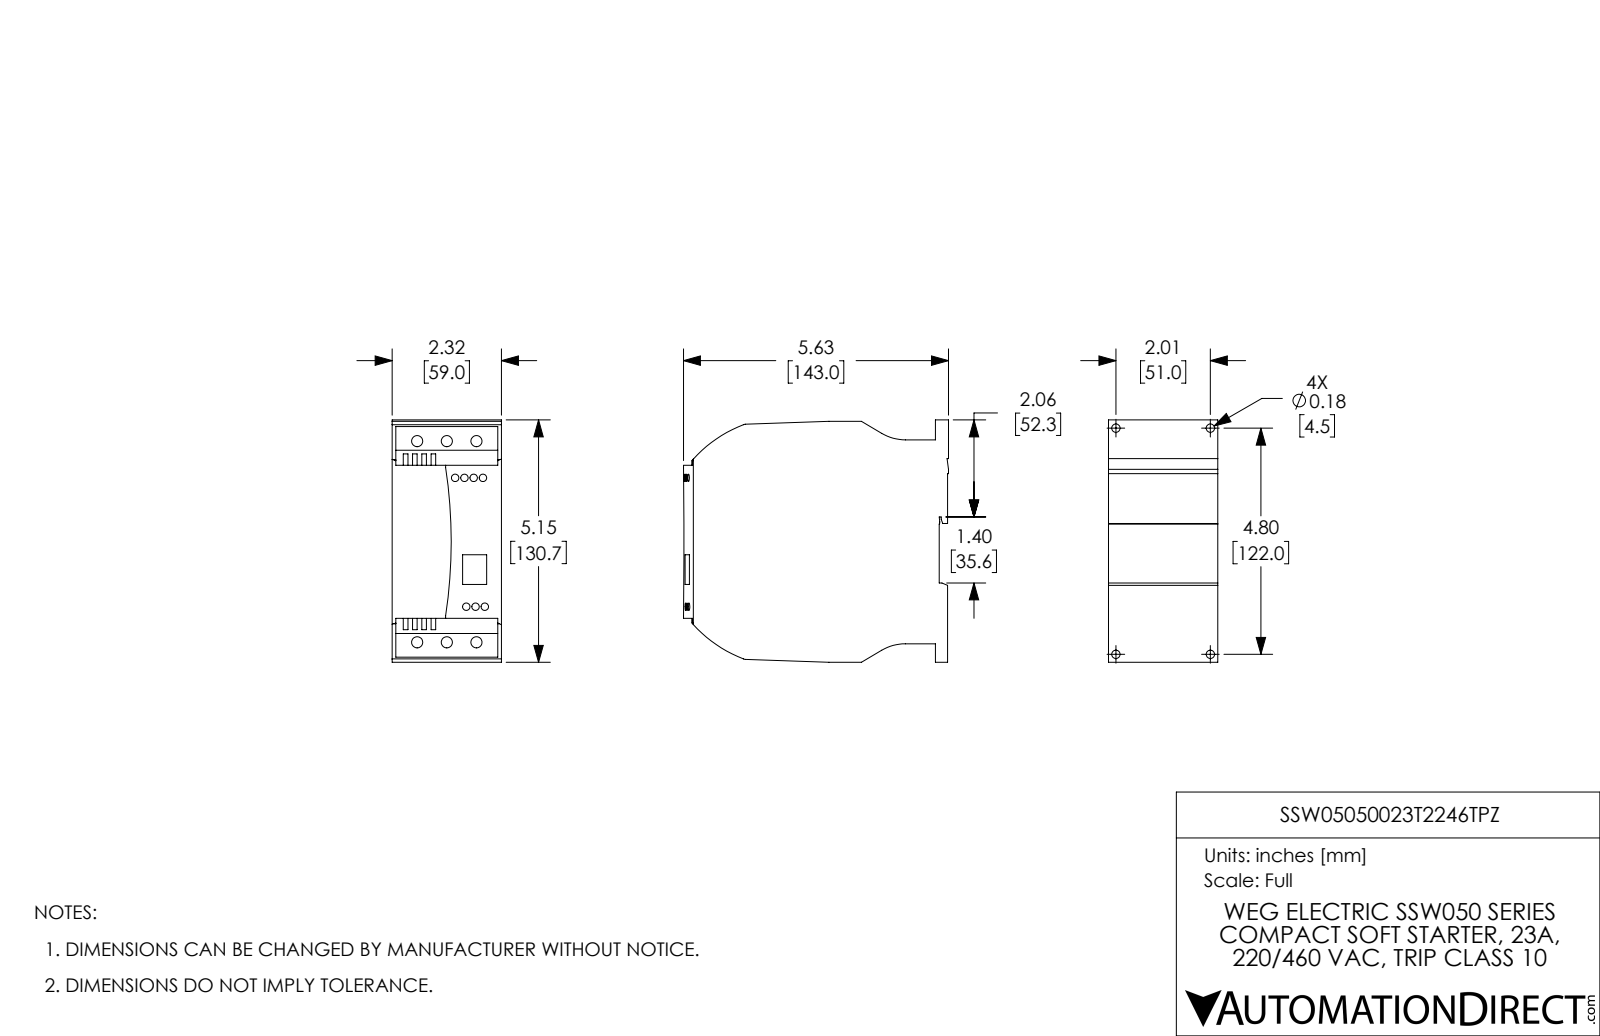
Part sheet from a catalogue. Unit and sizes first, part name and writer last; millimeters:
Units: millimetres
Overall size (bounding box): 143 × 130.7 × 59
Round holes (diameter × count): ⌀4 ×7, ⌀6 ×6, ⌀4.5 ×4
Partial cylindrical surfaces — rounded edges, fillets, slot ends (radius × count): R2.5 ×2, R25 ×2, R70.3 ×2, R127.5 ×1, R130.3 ×1, R266.2 ×1
Main face-to-face distances: 59, 10, 5, 2.5, 2, 57, 6.5, 7.5, 16, 4.5
Hole centre spacings: 5, 16, 109.7, 10, 69.5, 69.7, 108.5, 11.5
Volume: 933 900 mm³ · Surface area: 79 550 mm²
Bodies: 1 solid, 178 faces (131 planar, 43 cylindrical, 4 other)
Part name (STEP PRODUCT): SSW05 MEC A
STEP written by: SolidWorks 2017 (AUTOMOTIVE_DESIGN)
